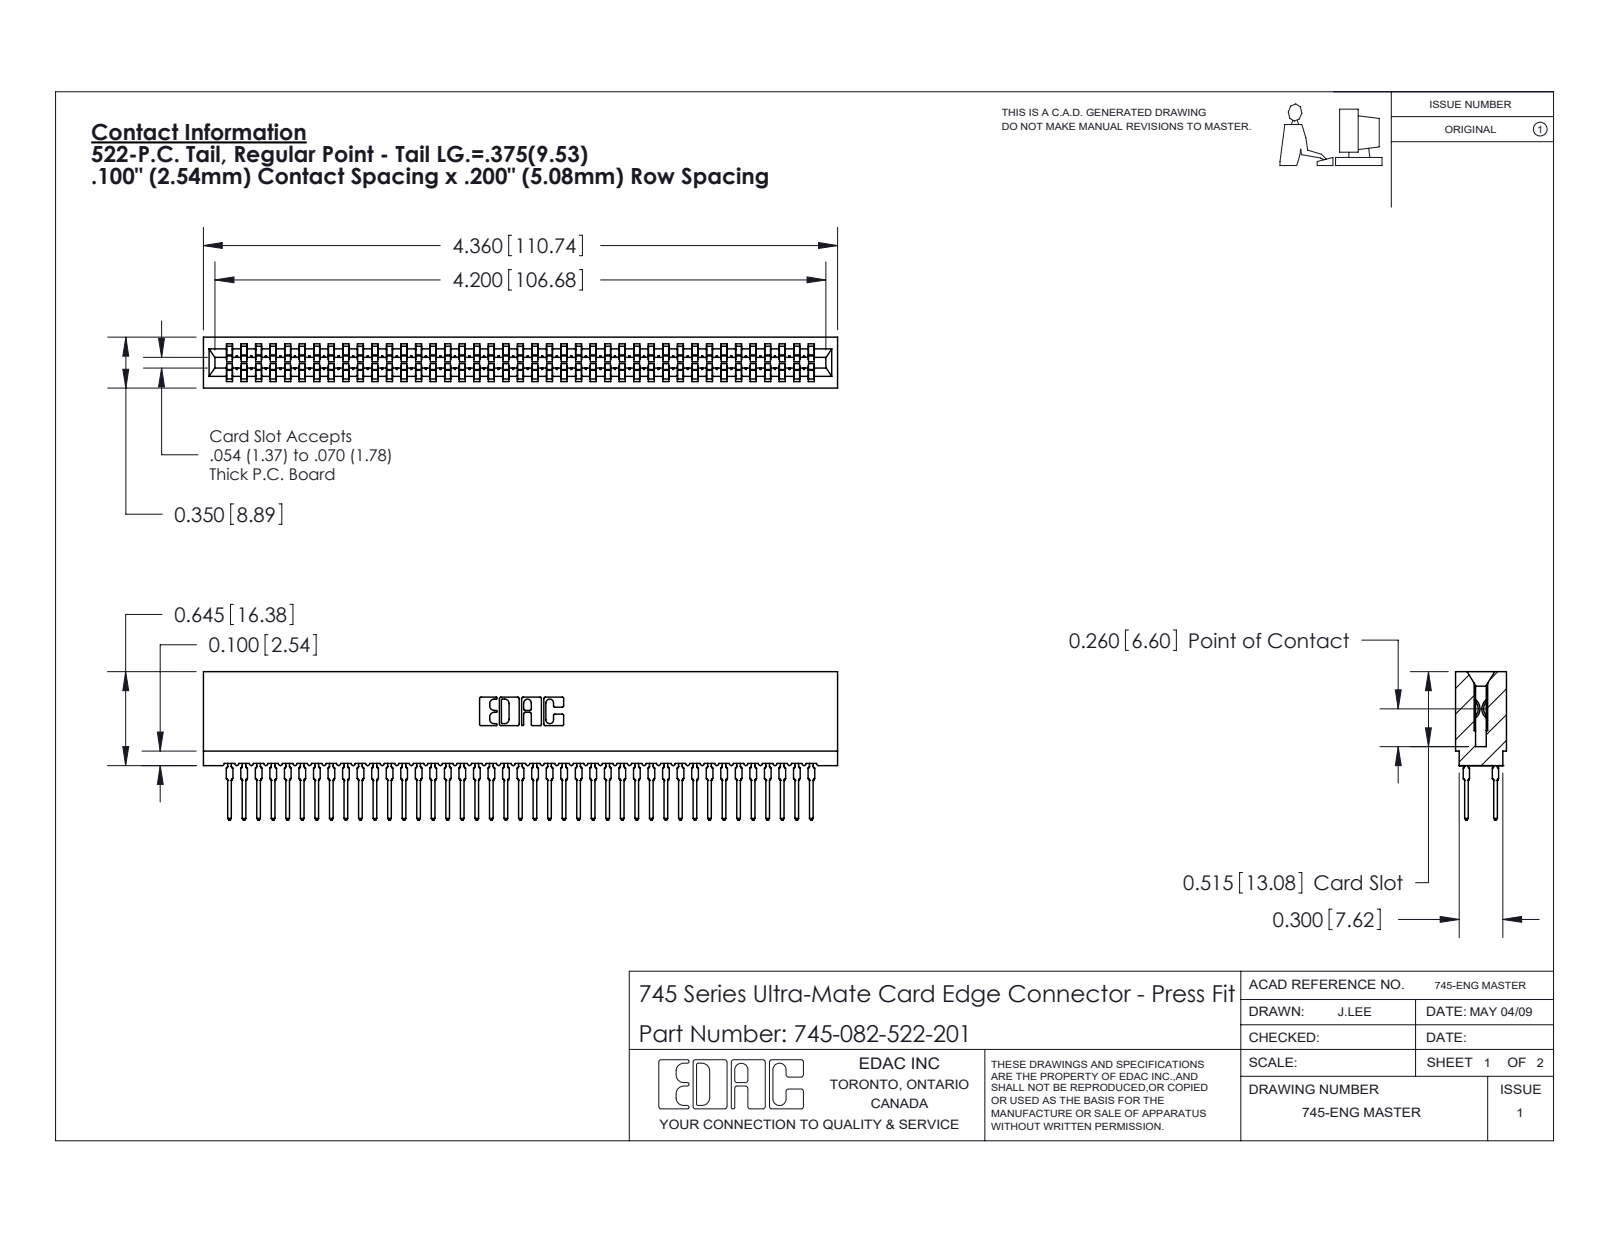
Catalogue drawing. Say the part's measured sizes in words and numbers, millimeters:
The part is named "745 Part_Insulator Option - 01; 745-082-522-201; 745-292-001_522". Its 3-D file was written by "SolidWorks 2020 (CONFIG_CONTROL_DESIGN)". It is 83 solids with 7434 faces: 3827 planar, 1475 cylindrical and 2132 other. Overall it measures 110.7 by 25.9 by 8.9 millimeters. Its volume is 10 100 cubic millimeters and its surface area 20 720 square millimeters. Partial cylindrical surfaces (rounded edges, fillets, slot ends): 164 of radius 0.5, 82 of radius 0.4, 22 of radius 0.3, 8 of radius 0.1, 8 of radius 0.3, 6 of radius 0.2, 6 of radius 0.8, 3 of radius 0.7. The main face-to-face distances are 8.9, 1.6, 7.3, 5.1, 3.5, 5.4, 1.9, 3.8, 1.1, 7.7.
